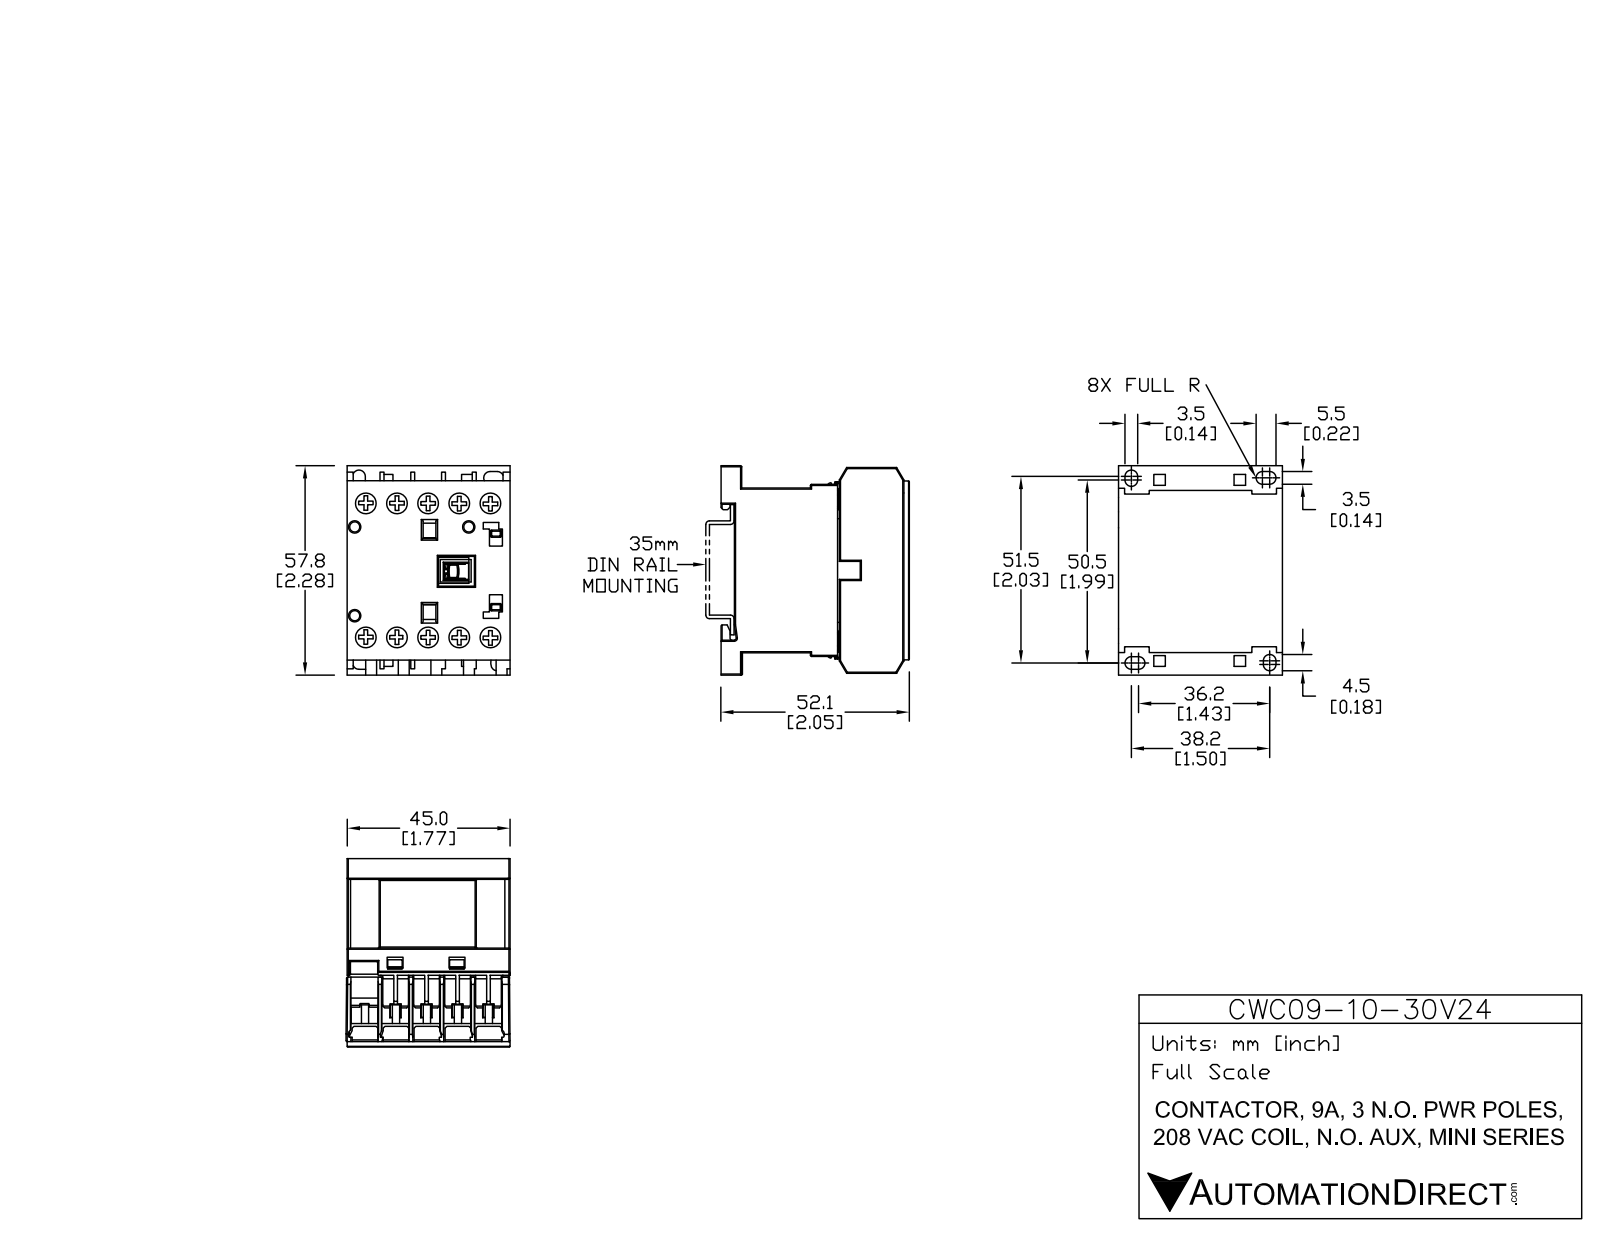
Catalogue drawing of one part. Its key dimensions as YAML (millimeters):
part_name: "CWC09-10-30V24"
step_written_by: "SolidWorks 2013 (AUTOMOTIVE_DESIGN)"
units: millimeters
bodies: {solids: 15, faces: 535, planar: 445, cylindrical: 90, other: 0}
overall_size: [58.04, 52.12, 45.75]
volume: 97133
surface_area: 30437
round_holes:
  - {diameter: 6.2, count: 10}
  - {diameter: 2.8, count: 3}
round_bosses_or_shafts:
  - {diameter: 5.9, count: 10}
partial_cylinders:
  - {radius: 0.3, count: 20}
  - {radius: 1.72, count: 6}
  - {radius: 1.73, count: 2}
  - {radius: 0.32, count: 1}
  - {radius: 0.42, count: 1}
  - {radius: 0.55, count: 1}
face_to_face_distances: [8.25, 45.5, 1.25, 16.5, 9.5, 5.5, 17.75, 5.13, 10.63, 7]
hole_center_spacings: [8.55, 37.94, 17.1, 40.72, 36.96, 25.65, 44.99, 6.91]
